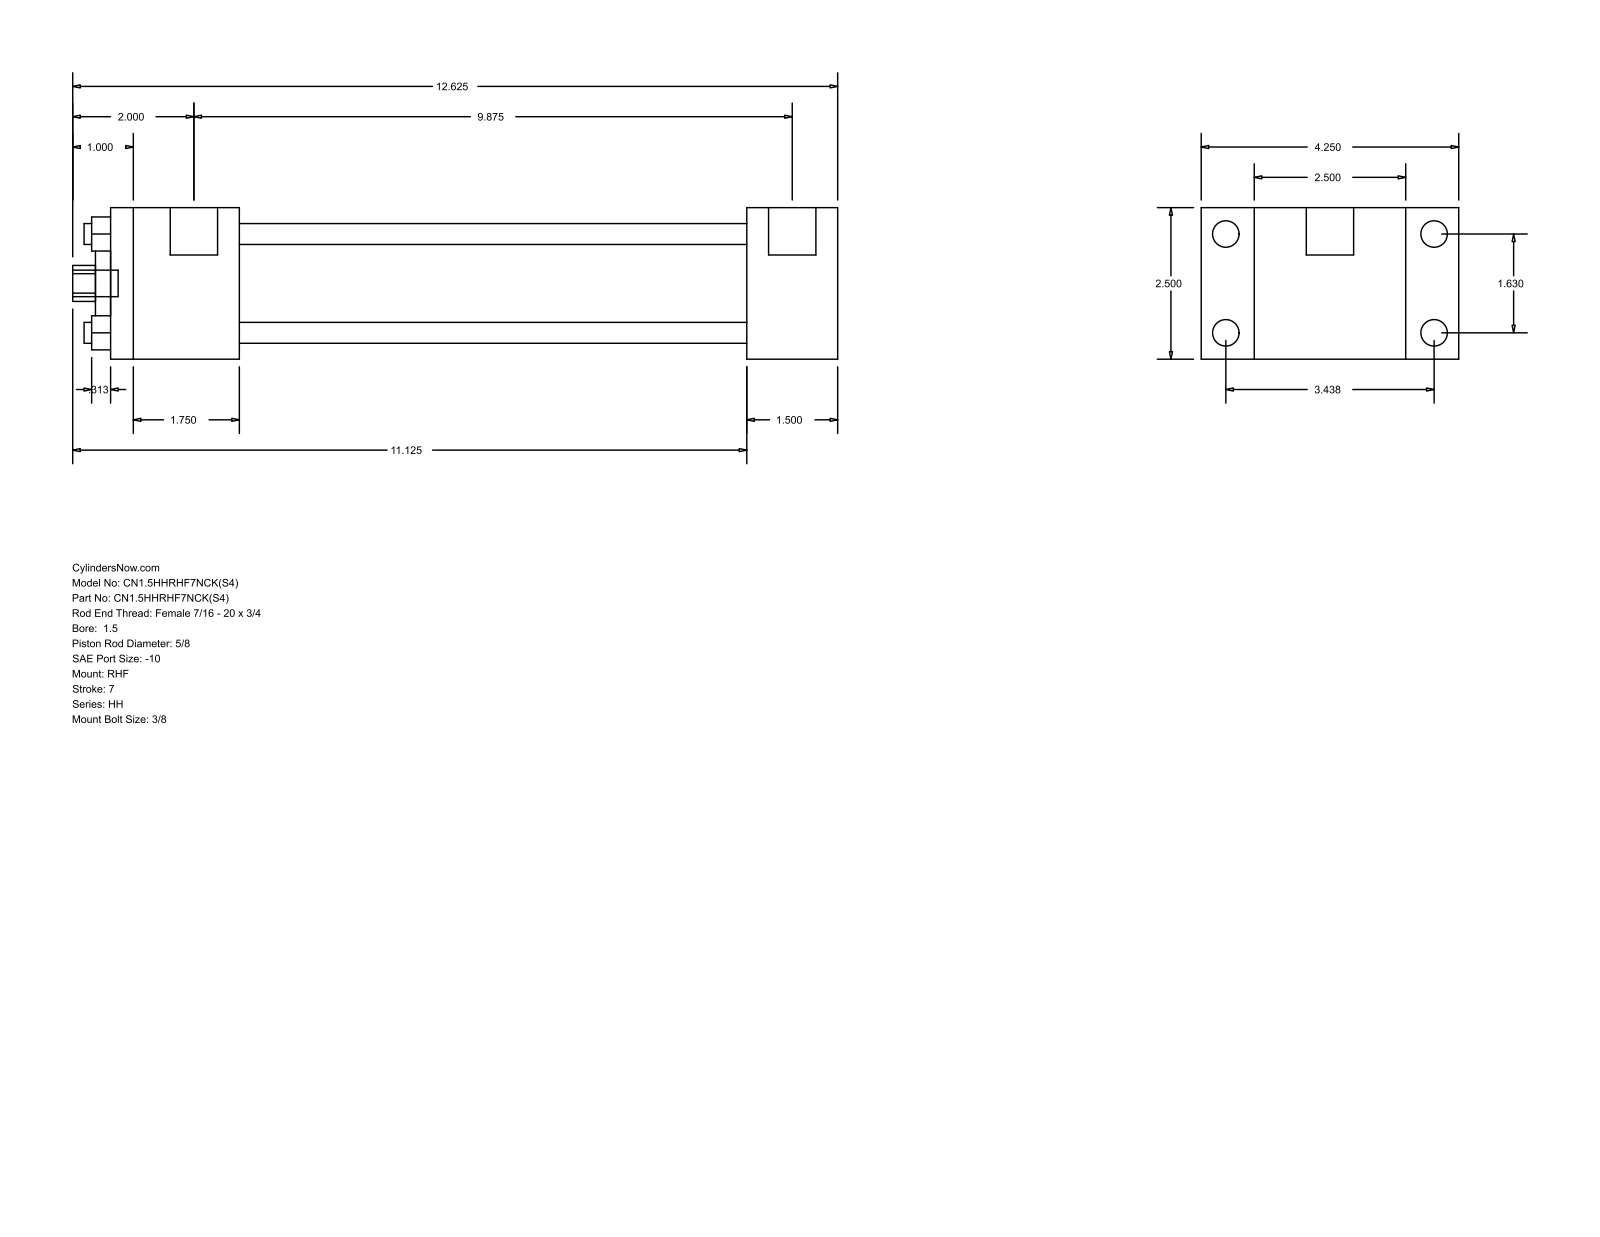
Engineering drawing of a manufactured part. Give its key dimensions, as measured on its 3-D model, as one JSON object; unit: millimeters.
{"part_name": "HH_RHF__0150_0.625", "step_written_by": "GSSL Pune (CONFIG_CONTROL_DESIGN)", "units": "millimeters", "bodies": {"solids": 0, "faces": 88, "planar": 60, "cylindrical": 28, "other": 0}, "overall_size": [320.68, 107.95, 63.5], "round_holes": [[8.76, 4], [15.88, 1], [28.57, 1], [44.45, 1]], "round_bosses_or_shafts": [[11.13, 4], [5.56, 4], [19.84, 2], [11.11, 1]], "partial_cylinders_radius": [[7.54, 1]], "face_to_face_distances": [63.5, 22.23, 85.73, 38.11, 266.69, 304.8, 107.96, 53.97, 212.72, 250.83], "hole_center_spacings": [29.27, 41.4, 58.55]}
